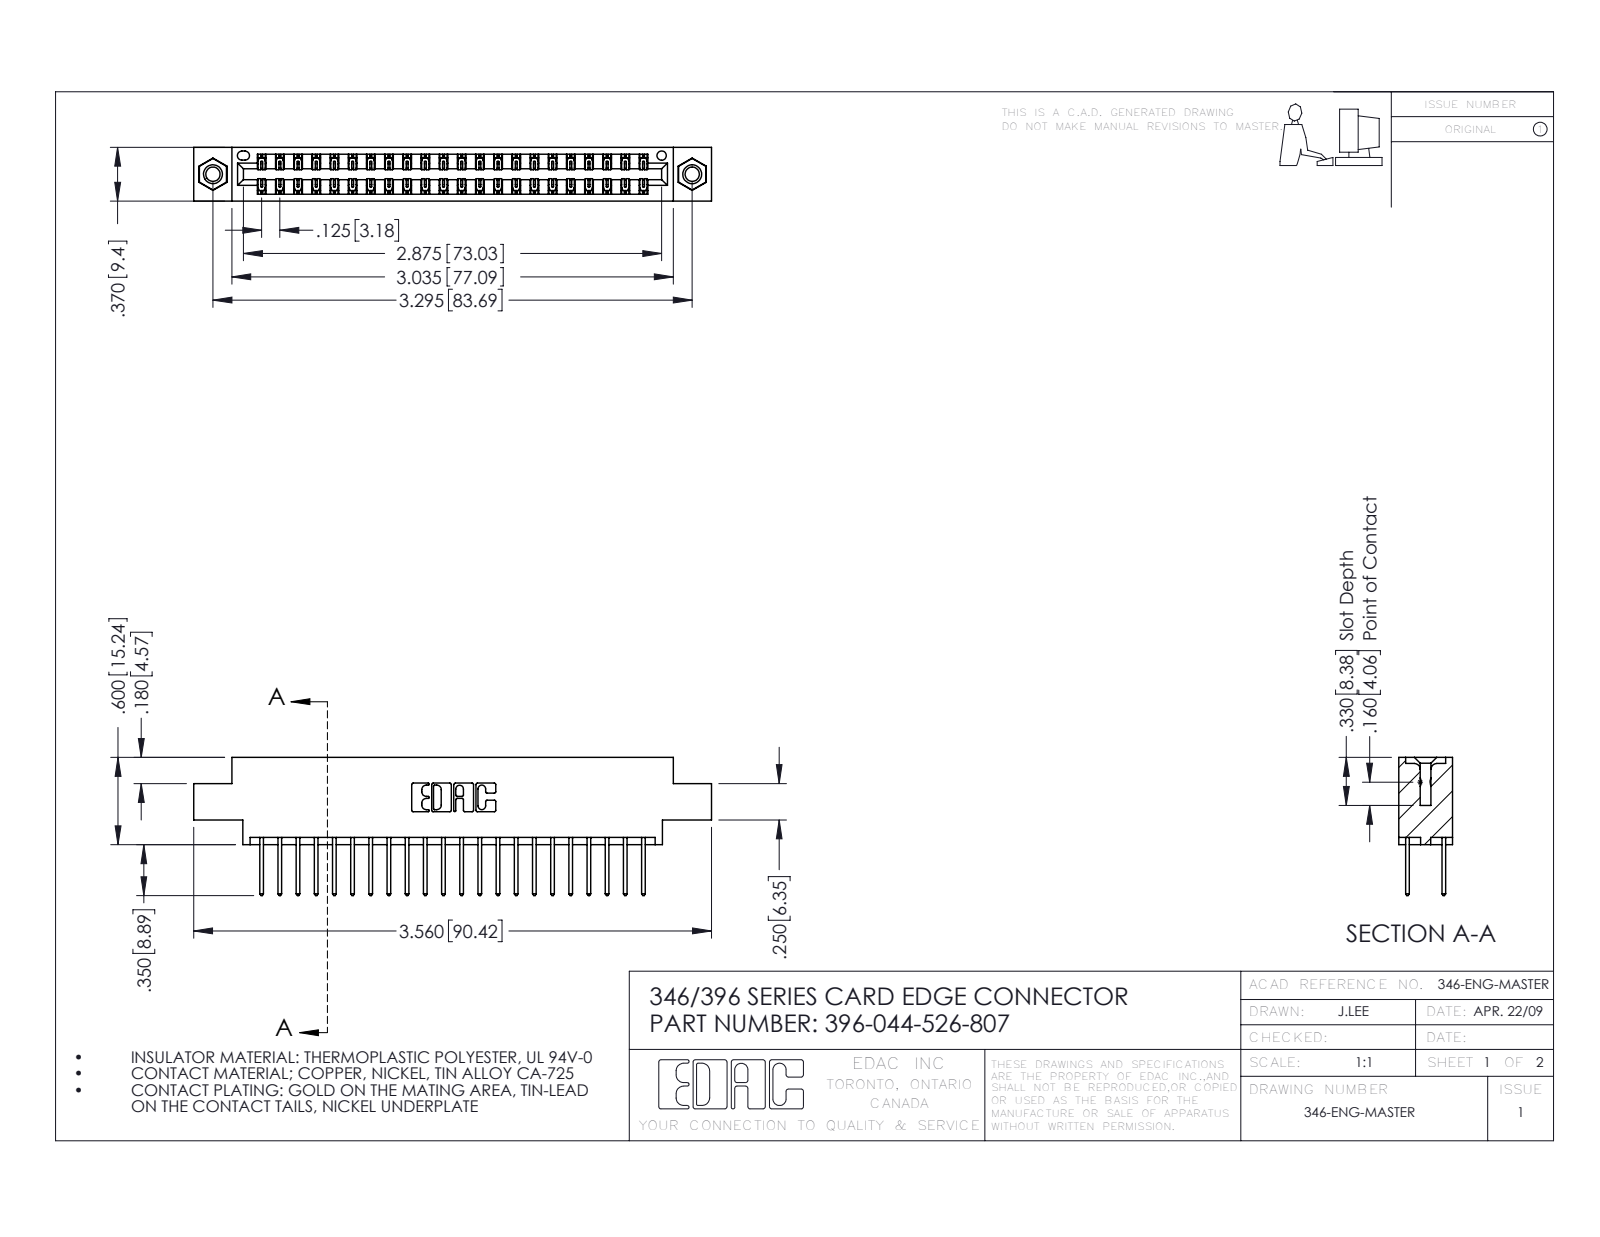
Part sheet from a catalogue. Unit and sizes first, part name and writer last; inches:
Units: inches
Overall size (bounding box): 3.56 × 0.95 × 0.37
Round holes (diameter × count): ⌀0.098 ×2, ⌀0.125 ×2, ⌀0.156 ×2, ⌀0.064 ×1
Round bosses / shafts (diameter × count): ⌀0.155 ×2
Partial cylindrical surfaces — rounded edges, fillets, slot ends (radius × count): R0.006 ×66, R0.01 ×44, R0.01 ×22, R0.007 ×6, R0.031 ×6, R0.026 ×3, R0.014 ×2, R0.022 ×2
Main face-to-face distances: 0.048, 0.322, 0.25, 0.37, 0.072, 0.298, 0.025, 0.275, 0.222, 0.148
Hole centre spacings: 0.246, 3.087, 3.295
Volume: 0.523 in³ · Surface area: 18.59 in²
Bodies: 47 solids, 2474 faces (1652 planar, 806 cylindrical, 16 other)
Part name (STEP PRODUCT): 396-044-526-807; 345-292-001_345-293-126; 345-250-001_345-250-005-103; 346 Part_0.170 Offset - 0.156 Dia-TI
STEP written by: SolidWorks 2016 (CONFIG_CONTROL_DESIGN)
